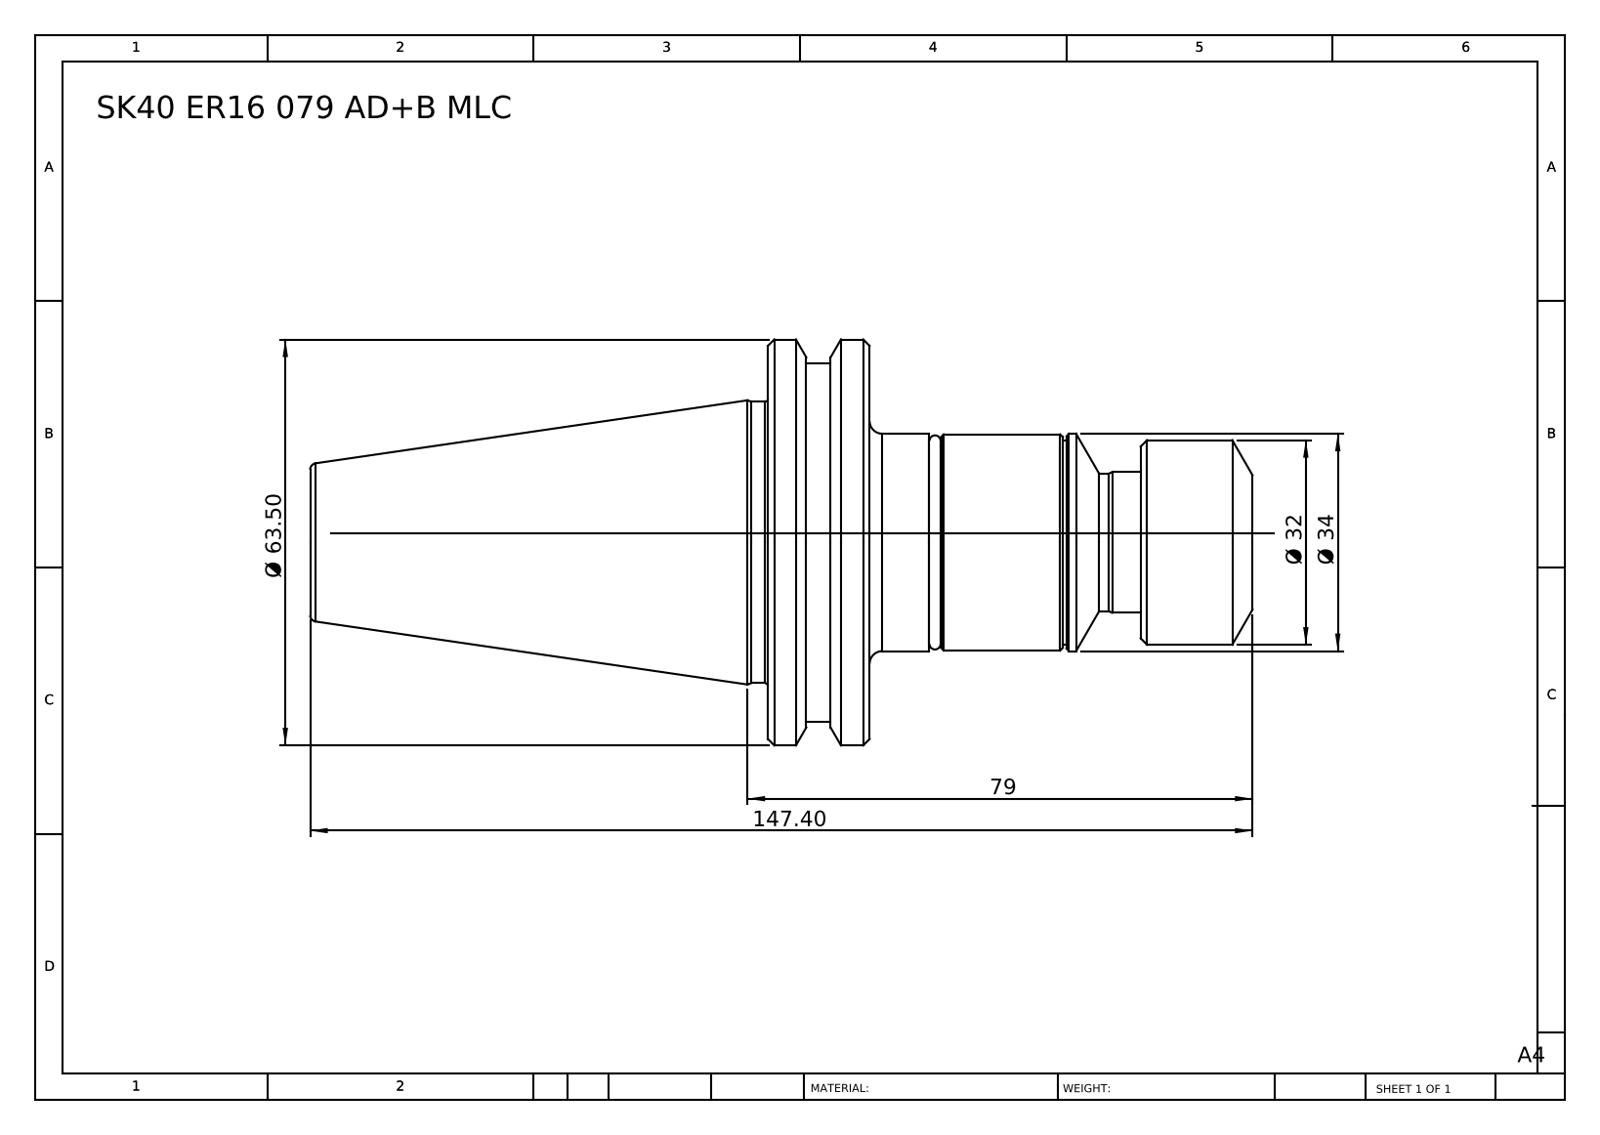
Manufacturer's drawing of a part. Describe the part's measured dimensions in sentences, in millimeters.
The part is named "SK 40 ER 16 079 AD+B MLC". Its 3-D file was written by "SolidWorks 2014 (CONFIG_CONTROL_DESIGN)". It is 2 solids with 71 faces: 11 planar, 24 cylindrical and 36 other. Overall it measures 147.4 by 63.5 by 63.5 millimeters. Its volume is 163 985 cubic millimeters and its surface area 24 179 square millimeters. Round bosses or shafts: 1 of diameter 63.5, 1 of diameter 56, 1 of diameter 44, 1 of diameter 34, 1 of diameter 33.8, 1 of diameter 32, 1 of diameter 29.9, 1 of diameter 22. The main face-to-face distances are 15.9, 87.5, 71.6, 59.9, 75.8, 147.4, 17.5, 42.4, 58.3, 129.9.
